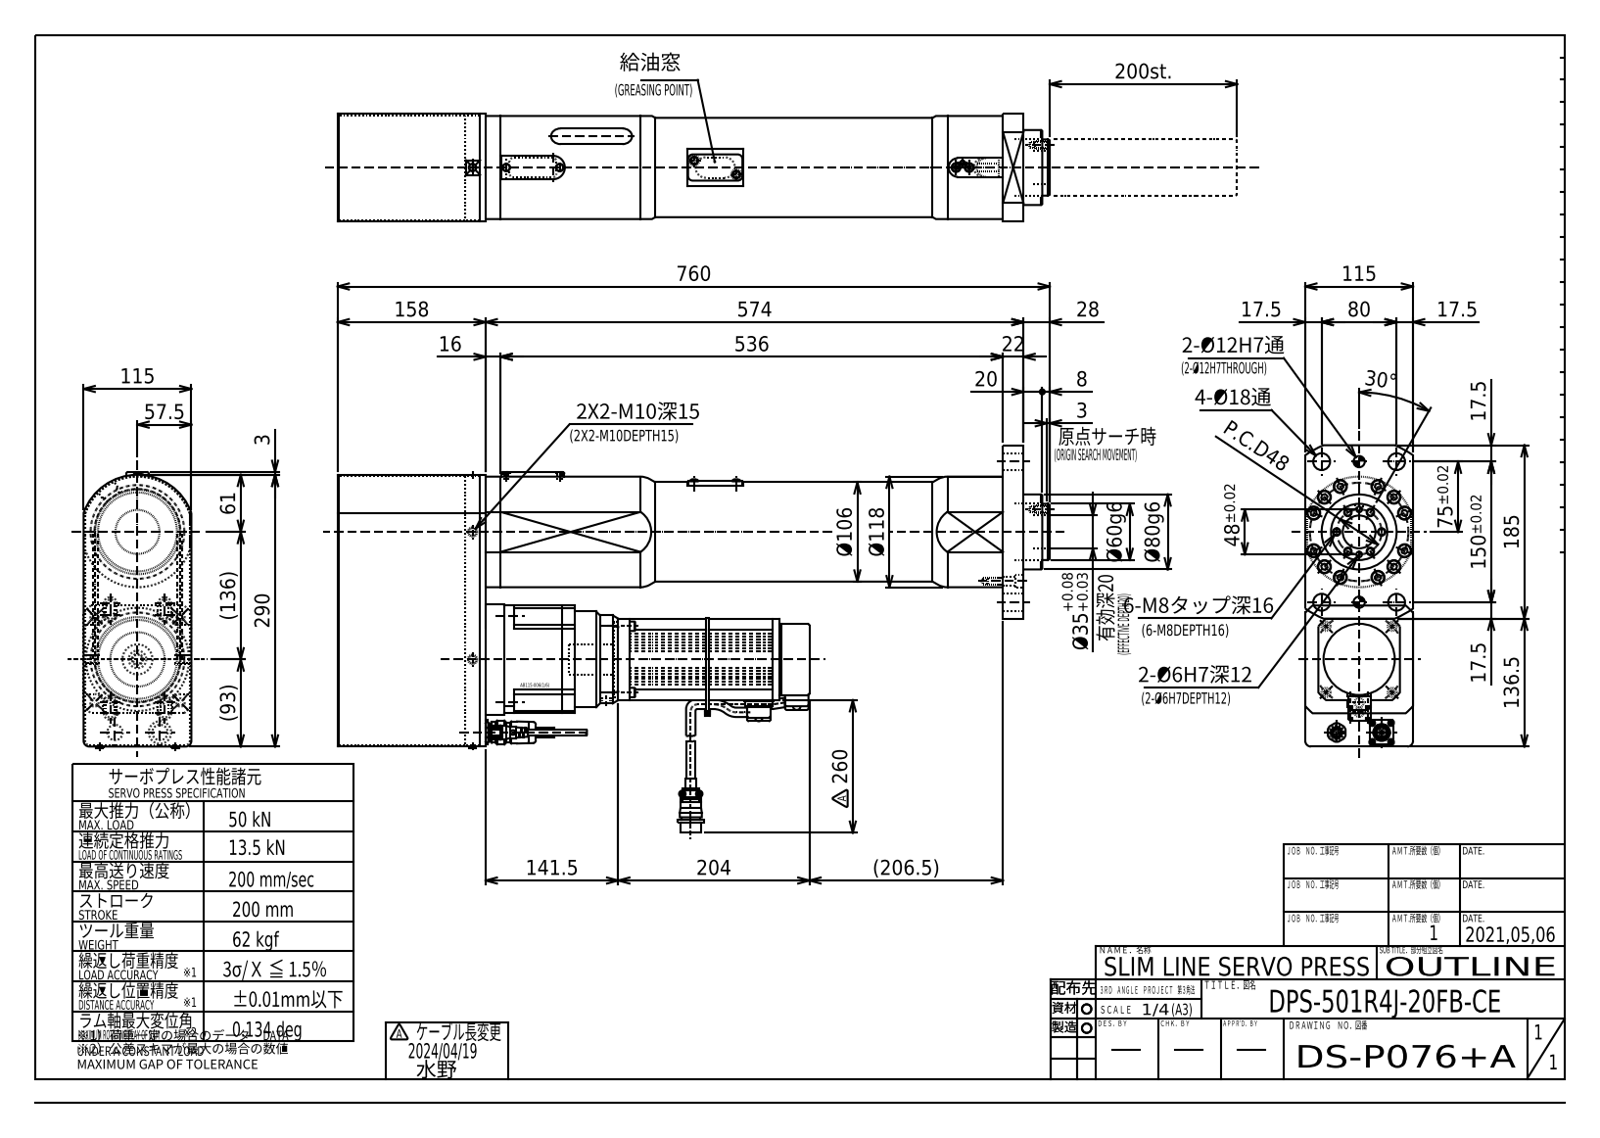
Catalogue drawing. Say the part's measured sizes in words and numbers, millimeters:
The part is named "DPS-501R4J-20FB-CE(DS-P076)". Its 3-D file was written by "Autodesk Inventor 2021 (AP203_CONFIGURATION_CONTROLLED_3D_DESIGN_OF_MECHANICAL_PARTS_AND_ASSEMBLIES_MIM_LF)". It is 2 solids with 1930 faces: 1039 planar, 573 cylindrical and 318 other. Overall it measures 760 by 323 by 115 millimeters. Its volume is 13 710 000 cubic millimeters and its surface area 678 214 square millimeters. Round holes: 20 of diameter 6.65, 16 of diameter 9, 12 of diameter 14, 4 of diameter 6.6, 4 of diameter 6.75, 4 of diameter 8.2, 4 of diameter 18, 3 of diameter 11, 2 of diameter 4.5, 2 of diameter 6, 2 of diameter 8, 2 of diameter 9.5. Round bosses or shafts: 25 of diameter 1, 17 of diameter 8, 16 of diameter 13, 6 of diameter 8.5, 5 of diameter 4, 4 of diameter 15.4, 4 of diameter 10, 4 of diameter 7.5. Partial cylindrical surfaces (rounded edges, fillets, slot ends): 48 of radius 0.6, 32 of radius 1, 20 of radius 0.3, 13 of radius 2.5, 12 of radius 4.25, 10 of radius 2, 10 of radius 5, 8 of radius 3. The main face-to-face distances are 115, 3, 1.5, 14, 101, 112.5, 2.5, 6, 4.5, 49.5. The hole center spacings are 24, 52.5, 74.24, 31.68, 48.66, 65.55, 75.23, 20.48.
